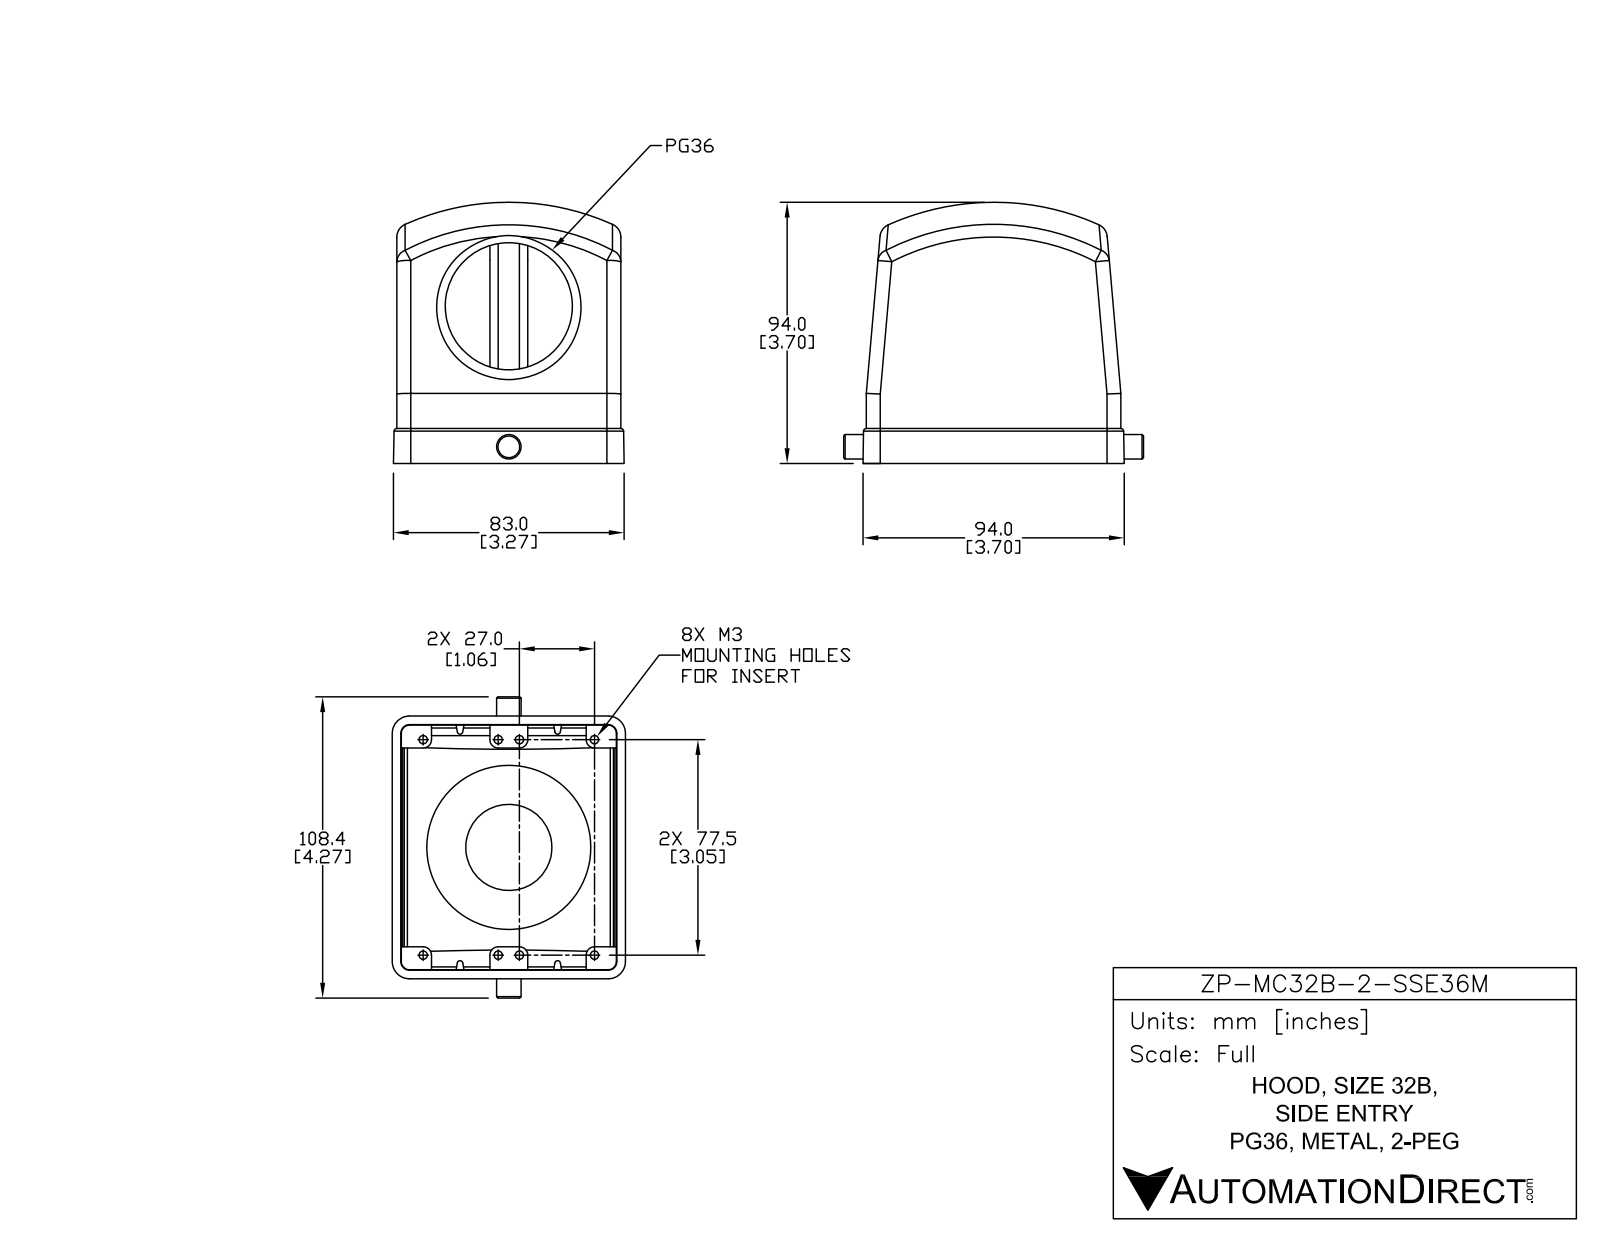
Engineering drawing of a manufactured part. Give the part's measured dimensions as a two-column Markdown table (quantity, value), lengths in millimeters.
| quantity | value |
| --- | --- |
| part name | ZP-MC32B-2-SSE36M |
| STEP written by | SolidWorks 2014 (AUTOMOTIVE_DESIGN) |
| units | millimeters |
| bodies | 2 solids, 219 faces (89 planar, 79 cylindrical, 51 other) |
| overall size | 108.35 × 92.75 × 83.9 |
| volume | 125 405 mm³ |
| surface area | 71 046 mm² |
| round holes (diameter × count) | 3 × 8, 2.6 × 1, 31 × 1, 45.72 × 1, 52 × 1 |
| round bosses / shafts (diameter × count) | 59 × 1, 8.8 × 1 |
| partial cylindrical surfaces (radius × count) | 3 × 9, 1 × 8, 5 × 8, 0.5 × 4 |
| main face-to-face distances | 3.1, 78.4, 81.5, 75.3, 10.3, 81.8, 5.58, 71.5, 83.28, 89 |
| hole center spacings | 27, 34.64, 38.94, 49.51, 77.5, 82.07, 84.89, 7.64 |
